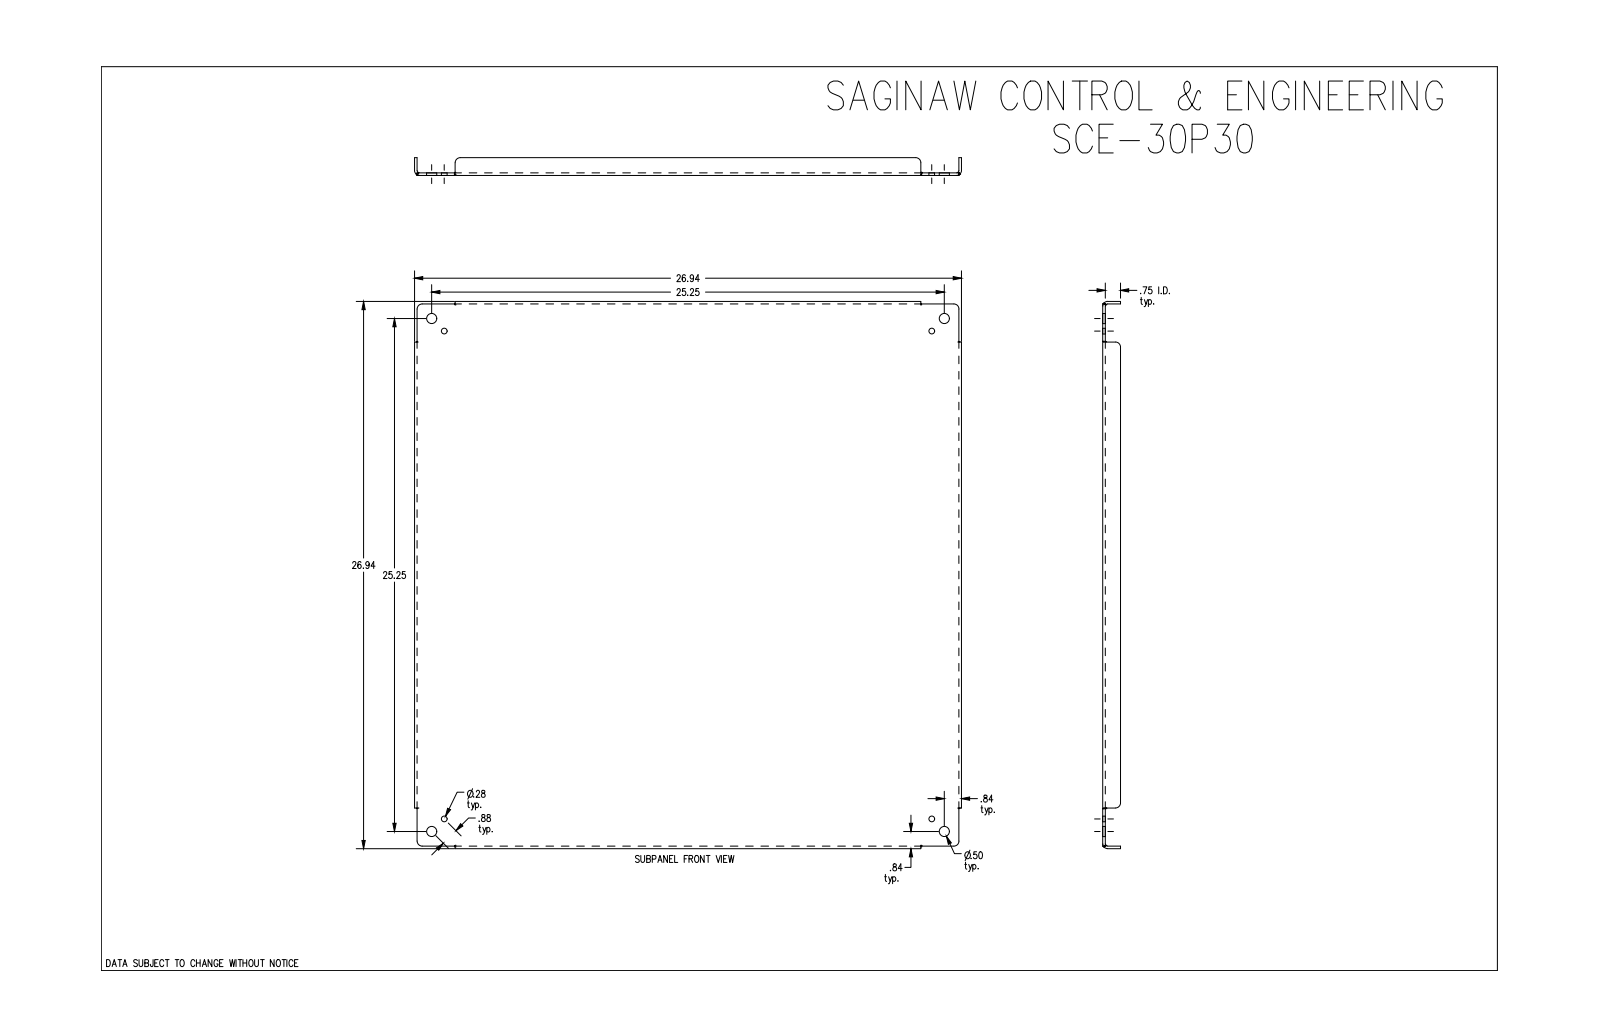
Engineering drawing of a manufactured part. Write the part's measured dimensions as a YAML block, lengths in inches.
part_name: "SCE-30P30"
step_written_by: "SolidWorks 2019 (CONFIG_CONTROL_DESIGN)"
units: inches
bodies: {solids: 1, faces: 82, planar: 30, cylindrical: 28, other: 24}
overall_size: [26.938, 26.938, 0.875]
volume: 98.05
surface_area: 1584
round_holes:
  - {diameter: 0.281, count: 4}
  - {diameter: 0.5, count: 4}
partial_cylinders:
  - {radius: 0.25, count: 8}
  - {radius: 0.112, count: 4}
  - {radius: 0.237, count: 4}
face_to_face_distances: [0.125, 0.125, 26.813, 26.687, 26.938, 0.75, 0.875, 2, 24.938, 1.875]
hole_center_spacings: [24.639, 0.875, 24.013, 25.25, 34.833, 33.959, 35.708]
